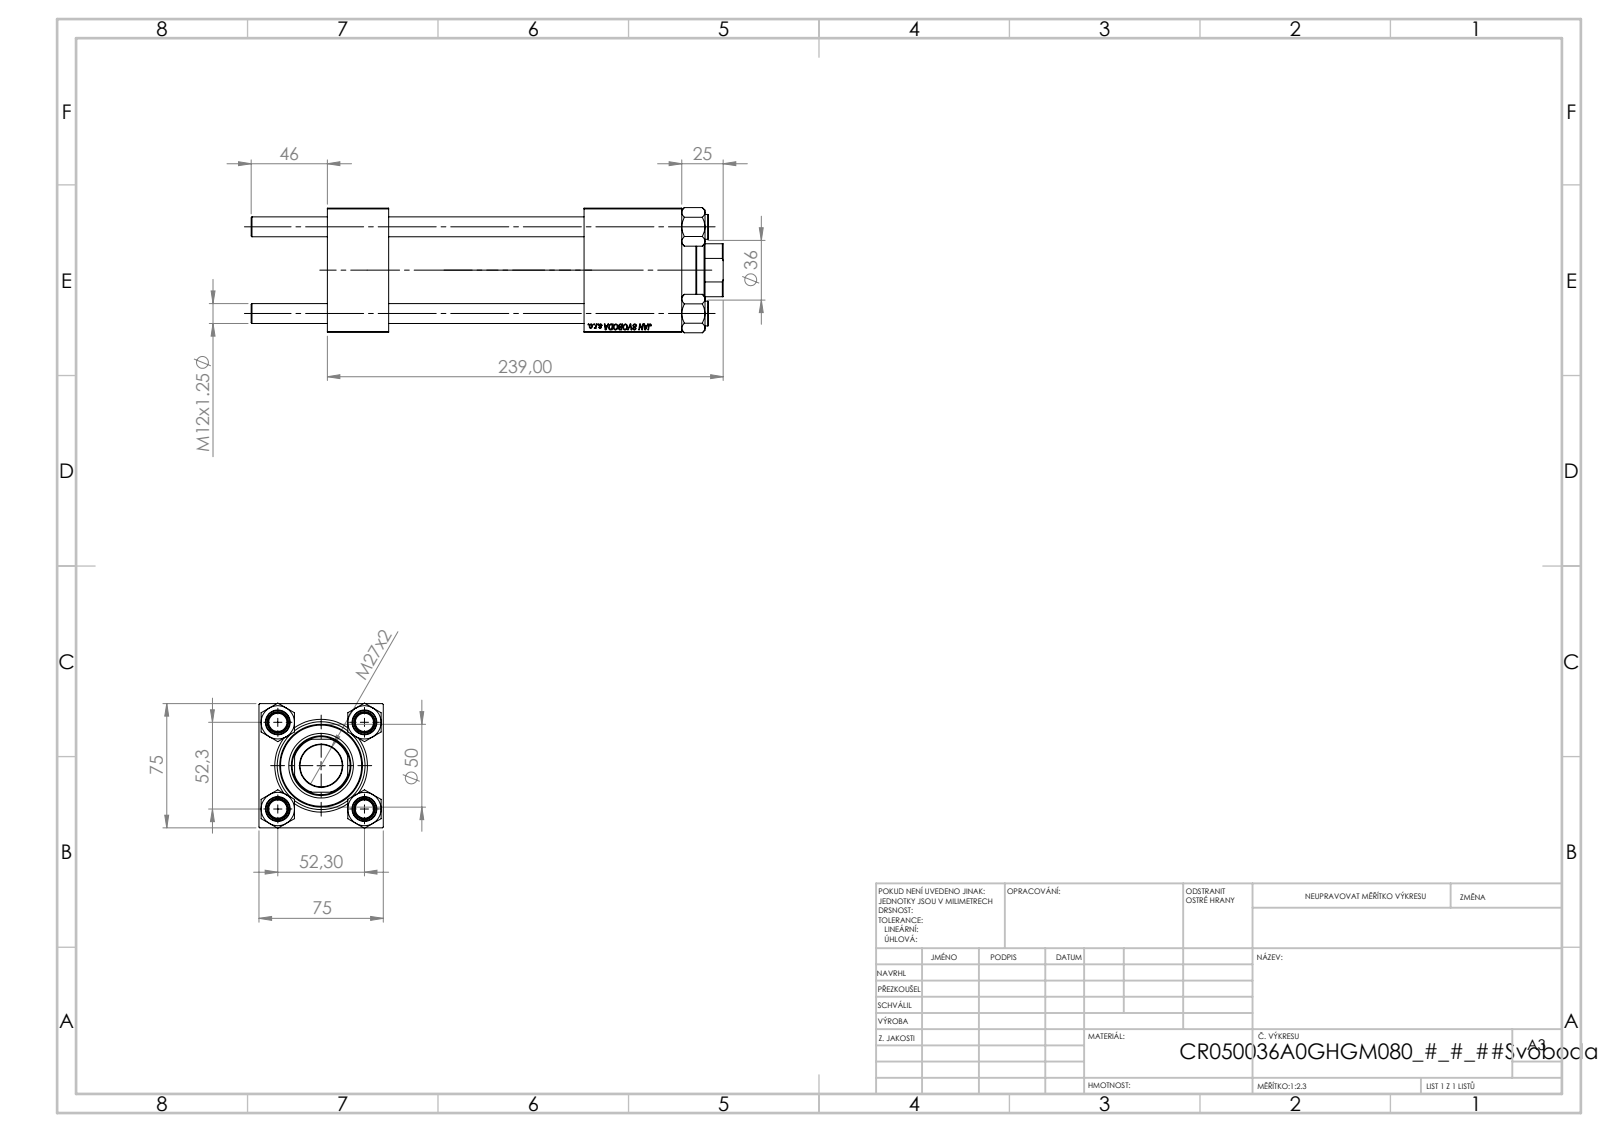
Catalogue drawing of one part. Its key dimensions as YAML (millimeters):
part_name: "NUT_M5; V215CR_BODY_A; CR025_012_A_0_G_A_G_M_020_+#_##_TYCINKA; V215CR_VCP (+1 more)"
step_written_by: "SolidWorks 2019 (CONFIG_CONTROL_DESIGN)"
units: millimeters
bodies: {solids: 11, faces: 1134, planar: 520, cylindrical: 78, other: 536}
overall_size: [285, 75.54, 75]
volume: 837356
surface_area: 207761
round_holes:
  - {diameter: 12, count: 4}
  - {diameter: 7, count: 2}
  - {diameter: 20.96, count: 2}
  - {diameter: 30, count: 2}
  - {diameter: 25.5, count: 1}
  - {diameter: 36, count: 1}
  - {diameter: 39, count: 1}
  - {diameter: 41, count: 1}
  - {diameter: 53, count: 1}
round_bosses_or_shafts:
  - {diameter: 15, count: 4}
  - {diameter: 56, count: 1}
  - {diameter: 50, count: 1}
partial_cylinders:
  - {radius: 17.5, count: 1}
face_to_face_distances: [75, 37, 155, 214, 177, 118, 59, 185.3, 148.3, 30.3]
hole_center_spacings: [36.98, 52.3, 73.96, 153.5]
